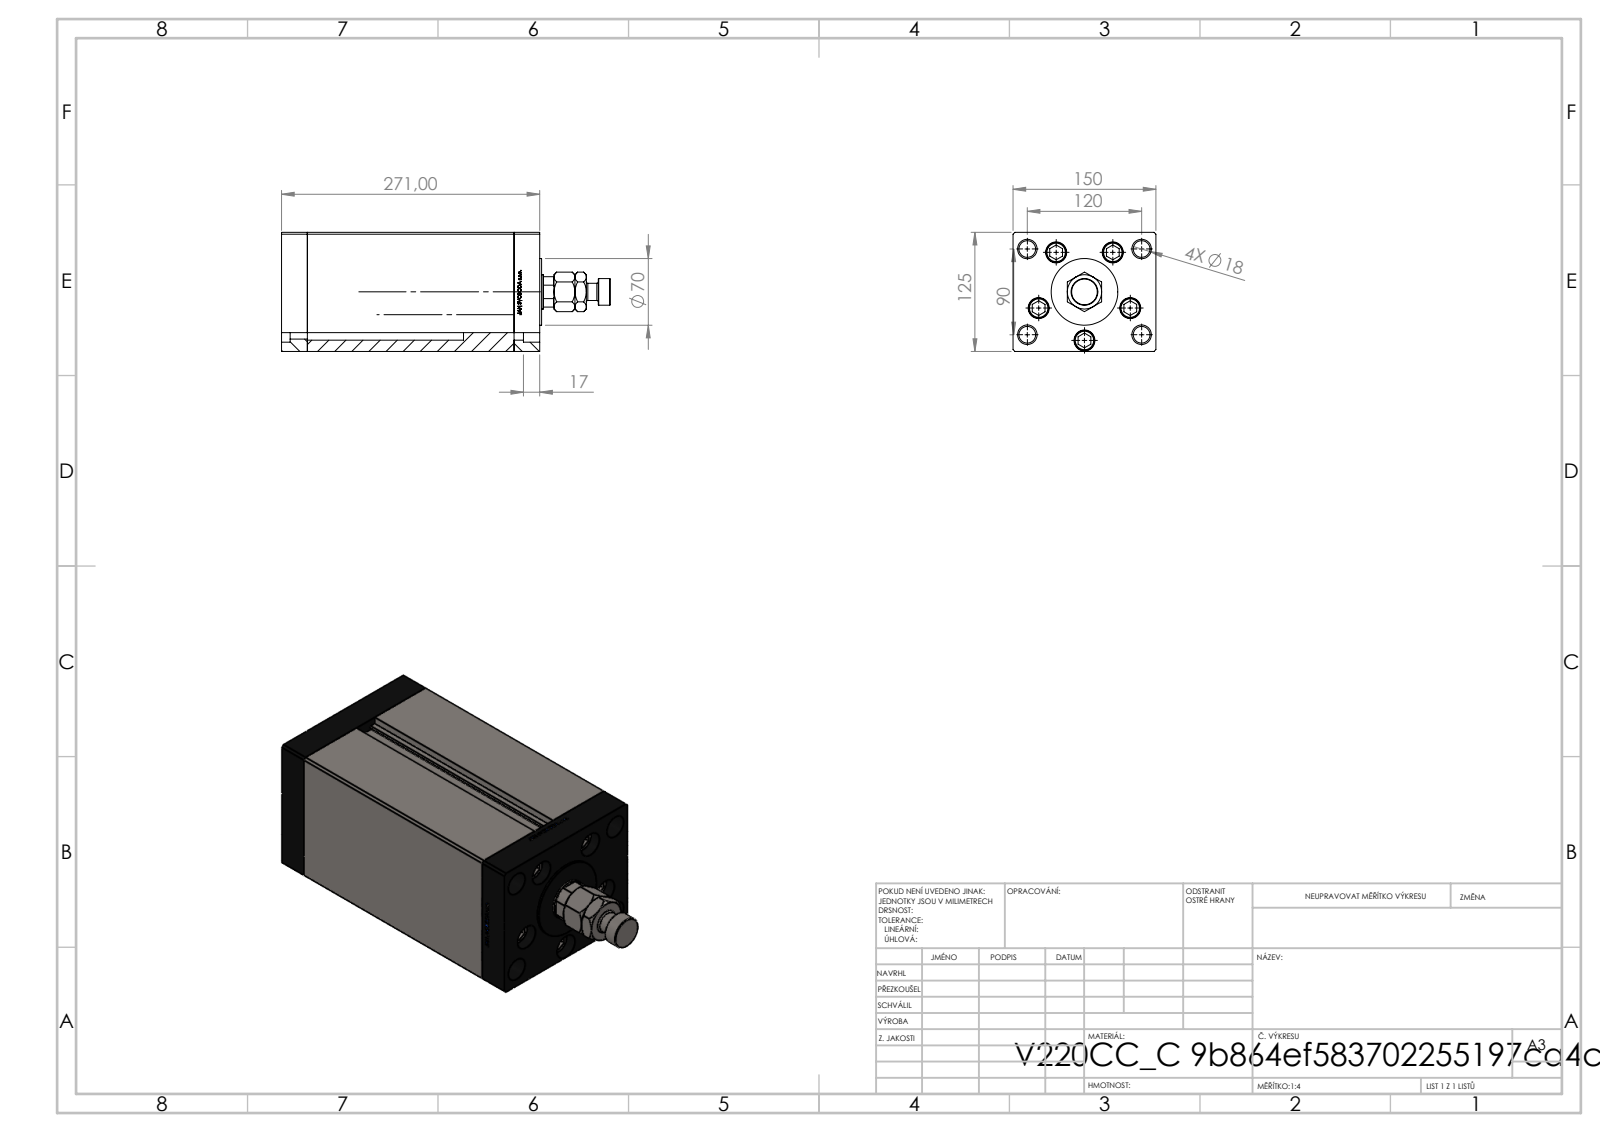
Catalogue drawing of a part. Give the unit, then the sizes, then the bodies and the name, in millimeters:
Units: millimetres
Overall size (bounding box): 345 × 150 × 125
Round holes (diameter × count): ⌀17.5 ×9, ⌀22 ×5, ⌀16 ×4, ⌀20.5 ×4, ⌀21 ×1, ⌀25.5 ×1, ⌀36 ×1
Round bosses / shafts (diameter × count): ⌀8 ×5, ⌀21 ×4, ⌀80 ×1, ⌀70 ×1, ⌀28 ×1, ⌀18 ×1
Partial cylindrical surfaces — rounded edges, fillets, slot ends (radius × count): R0.93 ×2, R17.5 ×1
Main face-to-face distances: 150, 125, 27, 244, 217, 33.5, 6.5, 271, 237.5, 210.5
Hole centre spacings: 51, 75, 30.43, 30.48, 58.89, 60.3, 61.25, 63.14
Volume: 4 176 000 mm³ · Surface area: 458 662 mm²
Bodies: 14 solids, 1215 faces (558 planar, 163 cylindrical, 494 other)
Part name (STEP PRODUCT): MFA; ALLEN BOLT; V220C_C MIDDLE; V220C BACK_C (+2 more)
STEP written by: SolidWorks 2019 (CONFIG_CONTROL_DESIGN)
